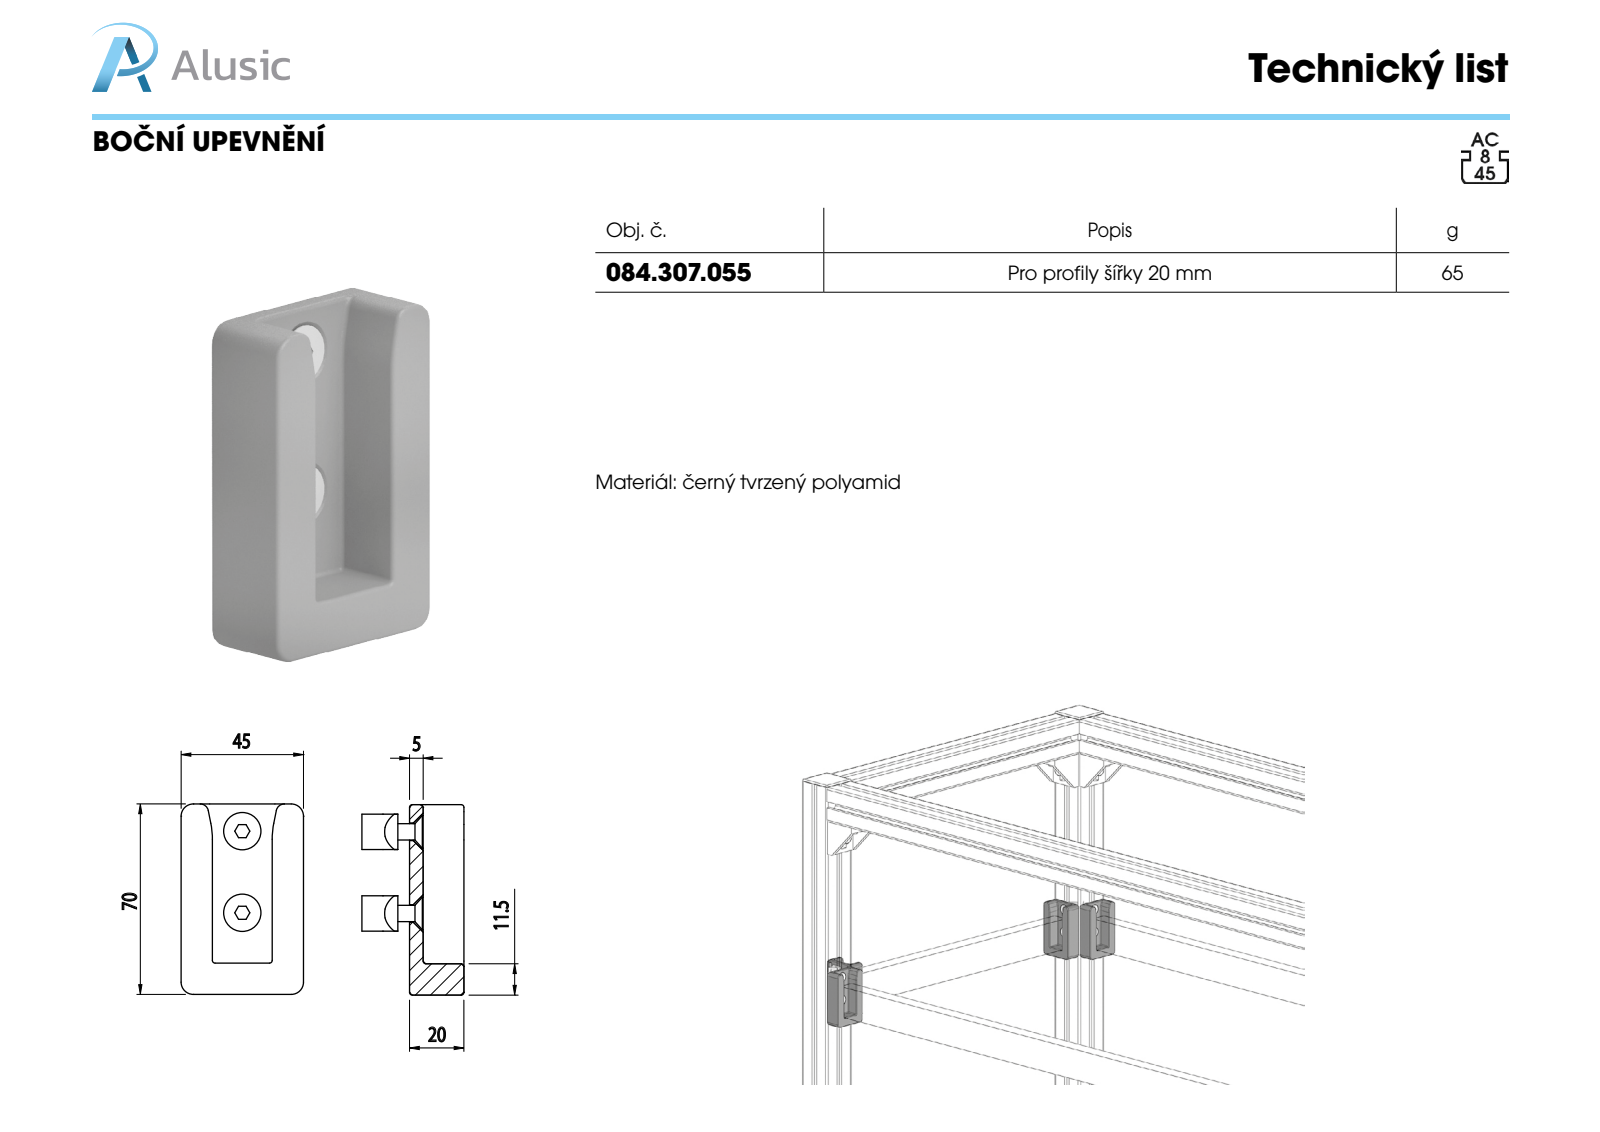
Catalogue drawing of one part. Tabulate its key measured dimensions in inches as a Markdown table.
| quantity | value |
| --- | --- |
| part name | 084.307.055 |
| STEP written by | SolidWorks 2012 (CONFIG_CONTROL_DESIGN) |
| units | inches |
| bodies | 1 solid, 196 faces (36 planar, 94 cylindrical, 66 other) |
| overall size | 2.756 × 1.772 × 0.787 |
| volume | 1.917 in³ |
| surface area | 26.33 in² |
| round holes (diameter × count) | 0.252 × 2 |
| partial cylindrical surfaces (radius × count) | 0.039 × 61, 0.177 × 6, 0.118 × 2, 1.181 × 2 |
| main face-to-face distances | 0.138, 0.315, 1.319, 0.453, 1.634, 0.177, 0.787, 1.457, 1.181, 1.004 |
| hole center spacings | 1.181 |
